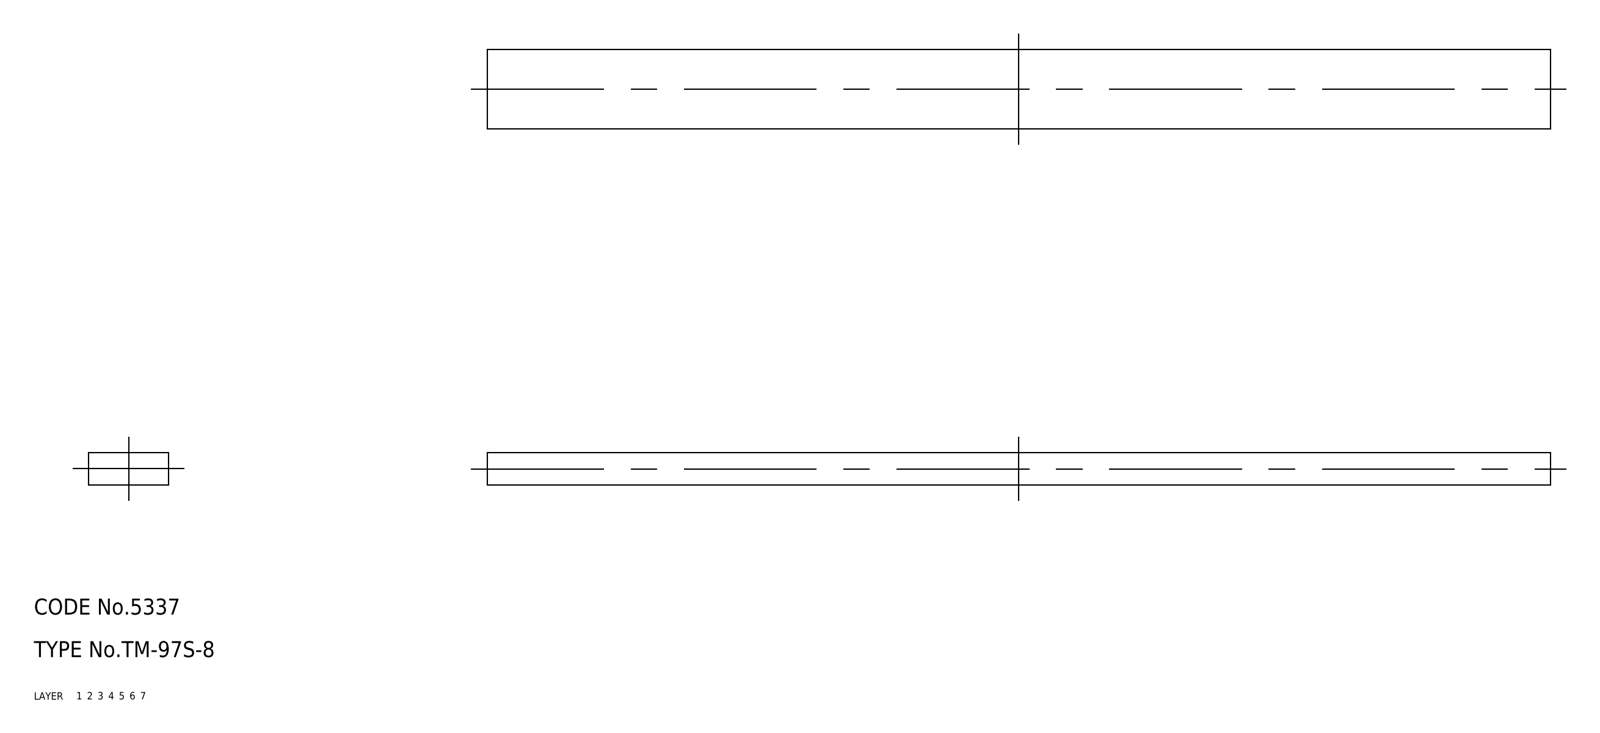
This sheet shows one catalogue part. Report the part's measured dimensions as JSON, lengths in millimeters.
{"part_name": "rubber foam", "step_written_by": "CADfix (AUTOMOTIVE_DESIGN)", "units": "millimeters", "bodies": {"solids": 1, "faces": 6, "planar": 0, "cylindrical": 0, "other": 6}, "overall_size": [200, 15, 6], "volume_mm3": 18000, "surface_area_mm2": 8580}
